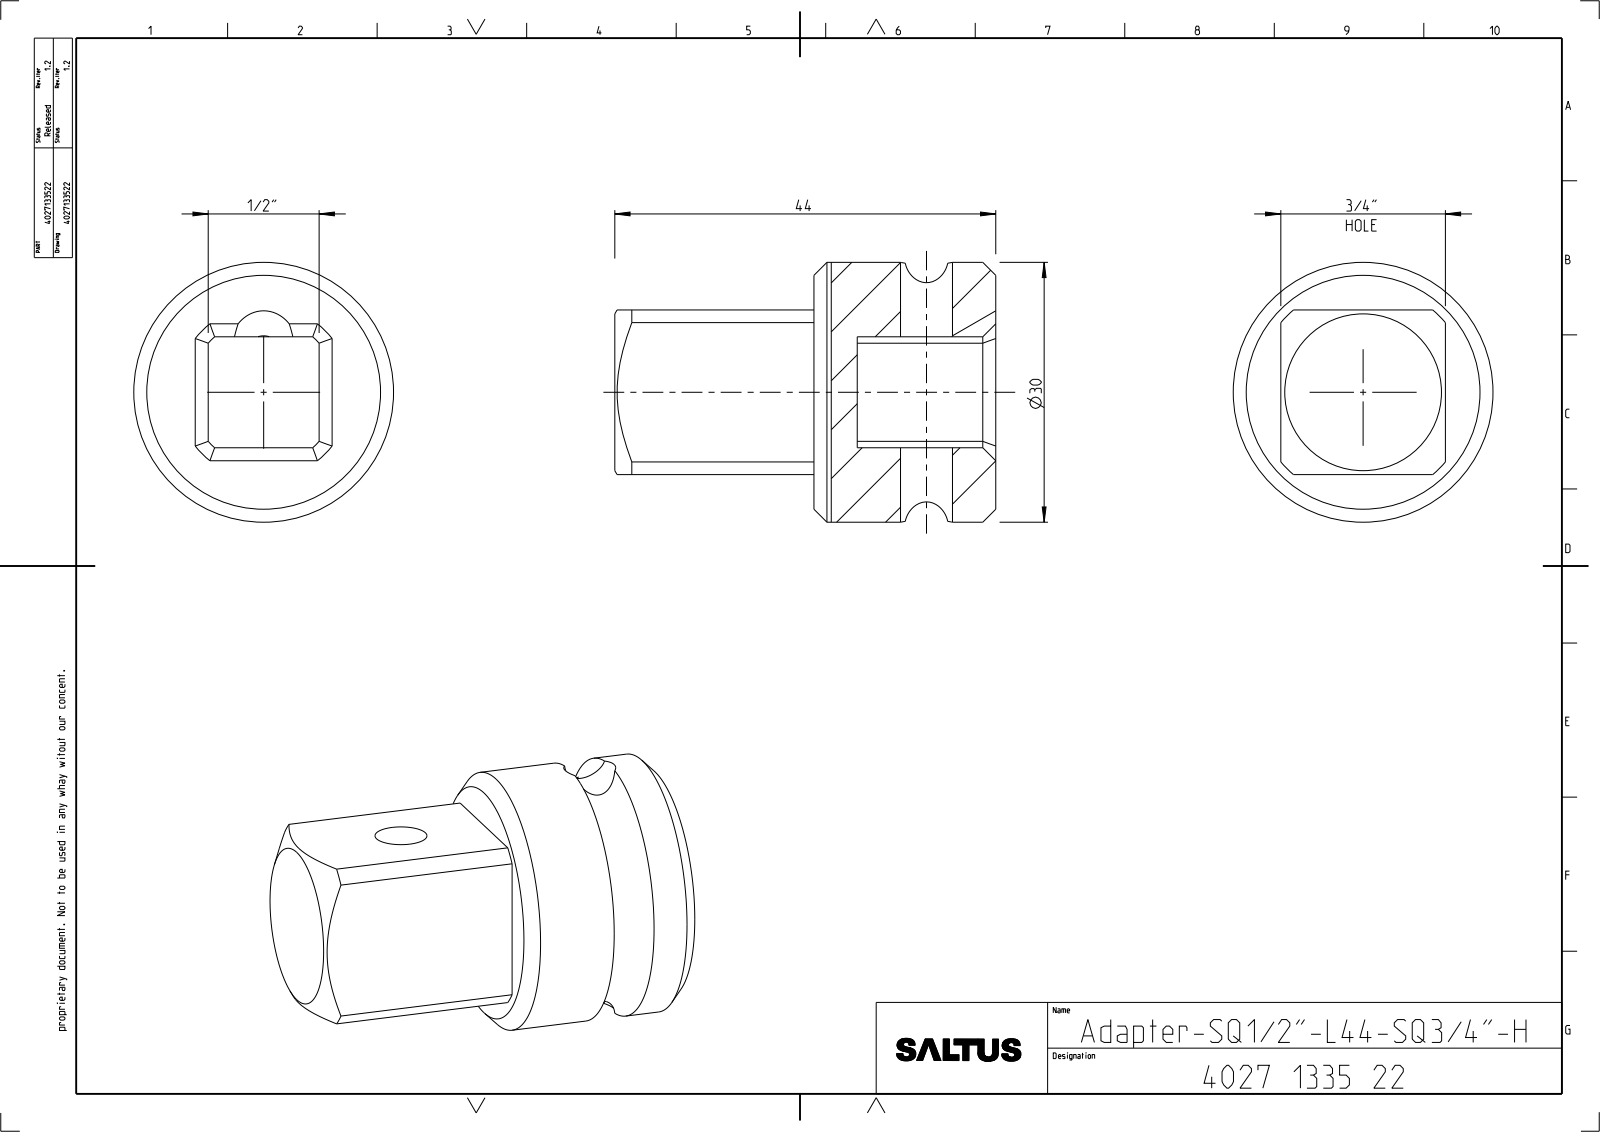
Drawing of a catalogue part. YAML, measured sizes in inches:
part_name: "4027133522"
step_written_by: "CREO PARAMETRIC BY PTC INC, 2022414 (CONFIG_CONTROL_DESIGN)"
units: inches
bodies: {solids: 1, faces: 48, planar: 17, cylindrical: 19, other: 12}
overall_size: [1.732, 1.181, 1.181]
volume: 1.129
surface_area: 9.564
round_holes:
  - {diameter: 0.236, count: 2}
round_bosses_or_shafts:
  - {diameter: 1.181, count: 1}
partial_cylinders:
  - {radius: 0.157, count: 1}
  - {radius: 0.337, count: 1}
  - {radius: 0.49, count: 1}
face_to_face_distances: [0.748, 0.122, 0.626, 0.505, 1.732, 0.827, 0.906, 0.63, 0.197, 1.102]
hole_center_spacings: [0.913]
